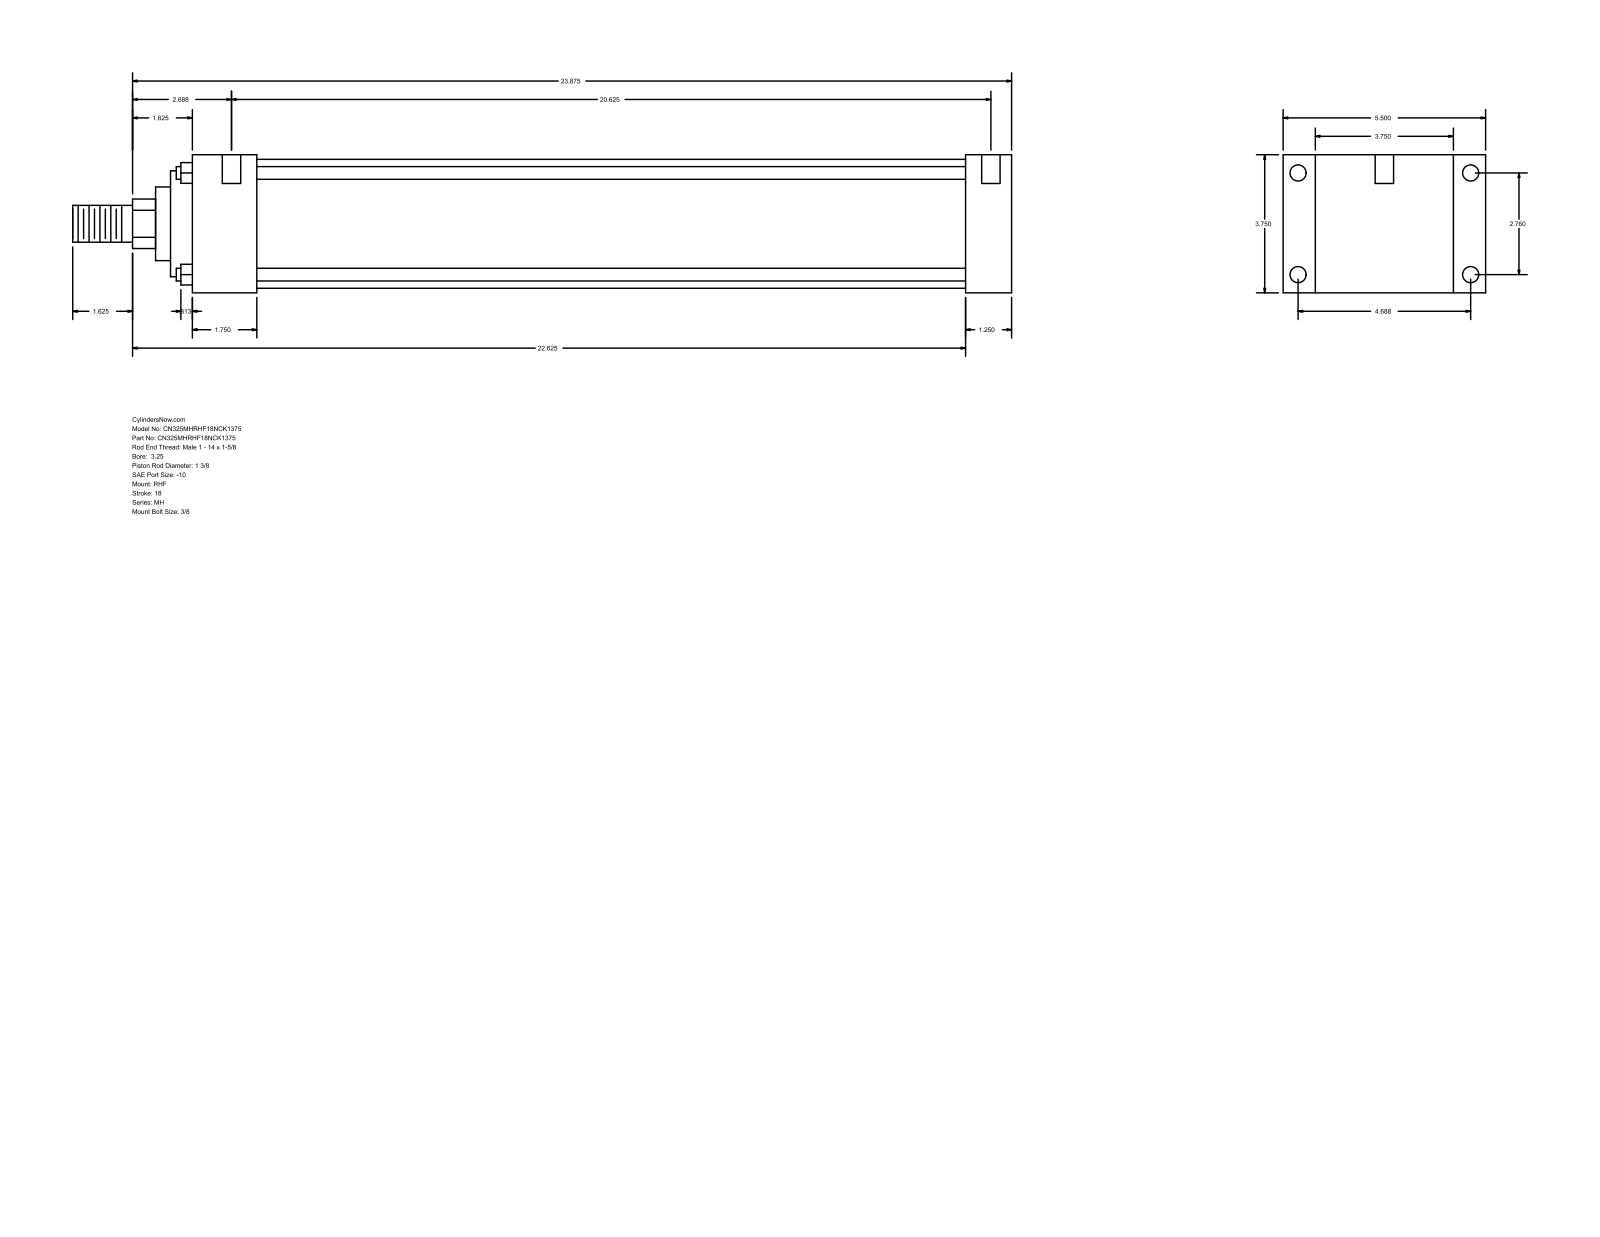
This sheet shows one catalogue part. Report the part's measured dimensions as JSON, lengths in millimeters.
{"part_name": "MH_RHF__0325_1.375", "step_written_by": "GSSL Pune (CONFIG_CONTROL_DESIGN)", "units": "millimeters", "bodies": {"solids": 0, "faces": 90, "planar": 61, "cylindrical": 29, "other": 0}, "overall_size": [647.7, 139.7, 95.25], "round_holes": [[5.56, 4], [11.13, 4], [12.7, 2]], "round_bosses_or_shafts": [[8.76, 4], [88.9, 1], [73.03, 1], [50.8, 1], [34.92, 1], [25.4, 1]], "partial_cylinders_radius": [[17.06, 1]], "face_to_face_distances": [95.24, 31.75, 22.23, 117.47, 533.4, 565.15, 139.7, 44.45, 488.95, 520.7], "hole_center_spacings": [70.1, 119.06, 138.16, 530.23, 1.59, 4.76, 523.88, 525.47]}
